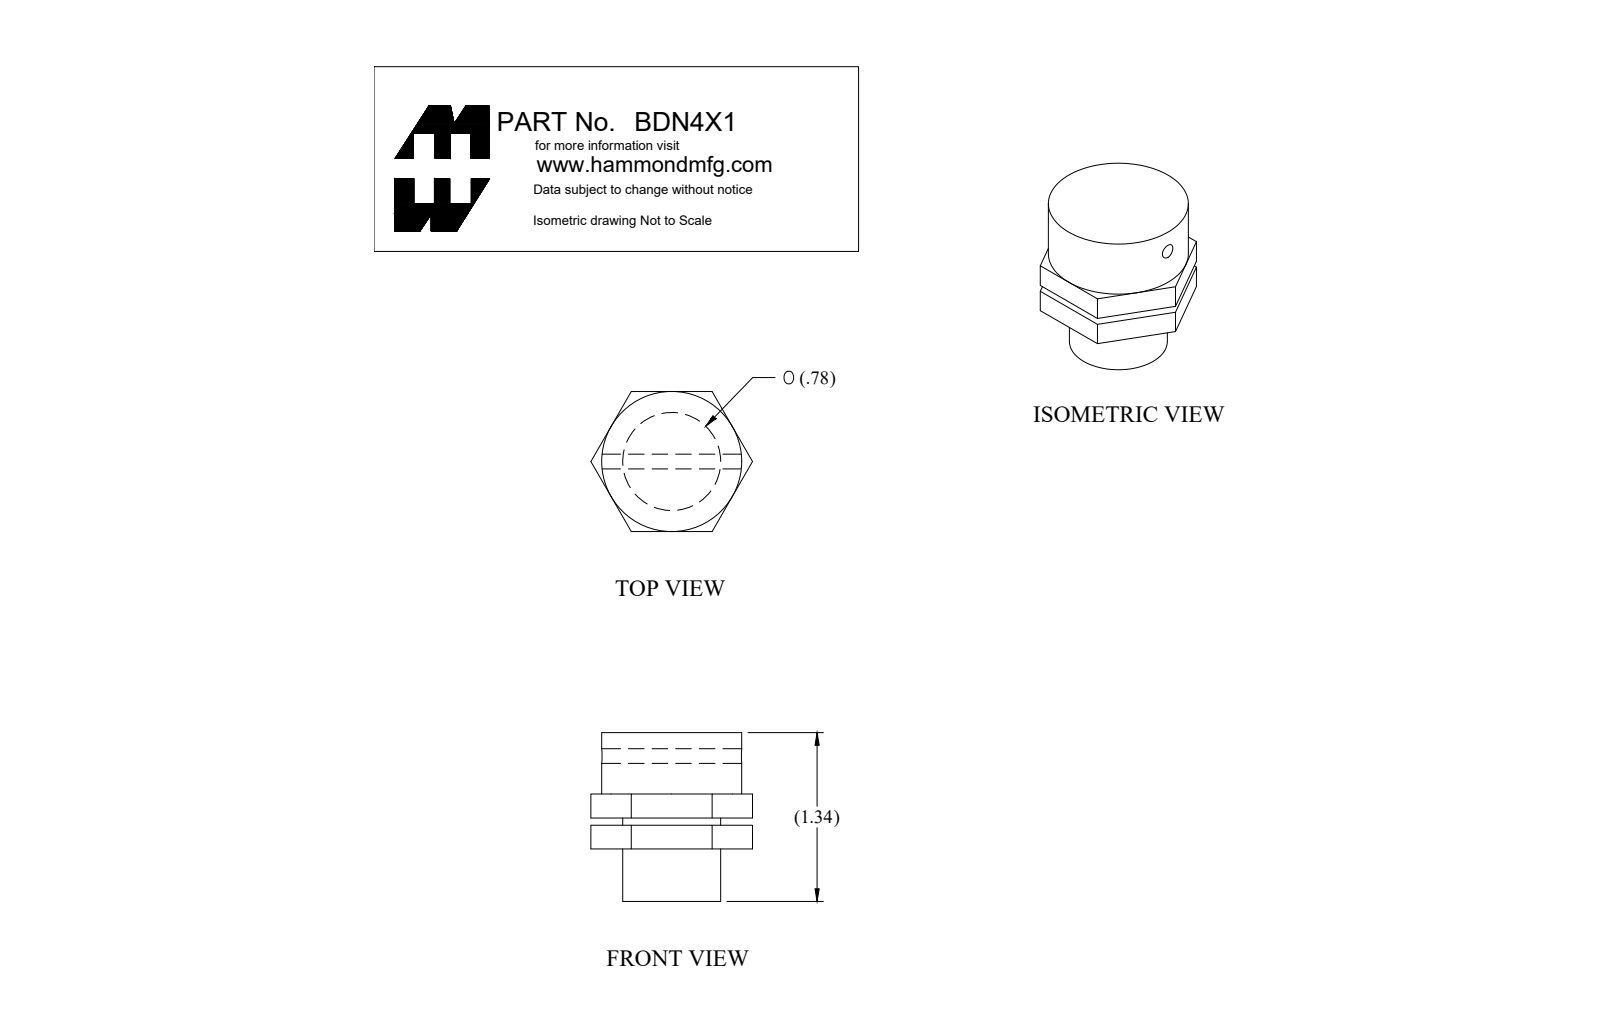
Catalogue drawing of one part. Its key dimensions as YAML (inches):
part_name: "BDN4XN1_Default"
step_written_by: "SolidWorks 2019 (CONFIG_CONTROL_DESIGN)"
units: inches
bodies: {solids: 1, faces: 31, planar: 23, cylindrical: 8, other: 0}
overall_size: [1.34, 1.284, 1.112]
volume: 1.092
surface_area: 8.039
round_holes:
  - {diameter: 0.117, count: 1}
round_bosses_or_shafts:
  - {diameter: 1.112, count: 1}
  - {diameter: 0.778, count: 1}
face_to_face_distances: [1.112, 0.735, 0.057, 0.678, 0.188, 0.245, 0.923, 0.417, 0.605, 0.662]
